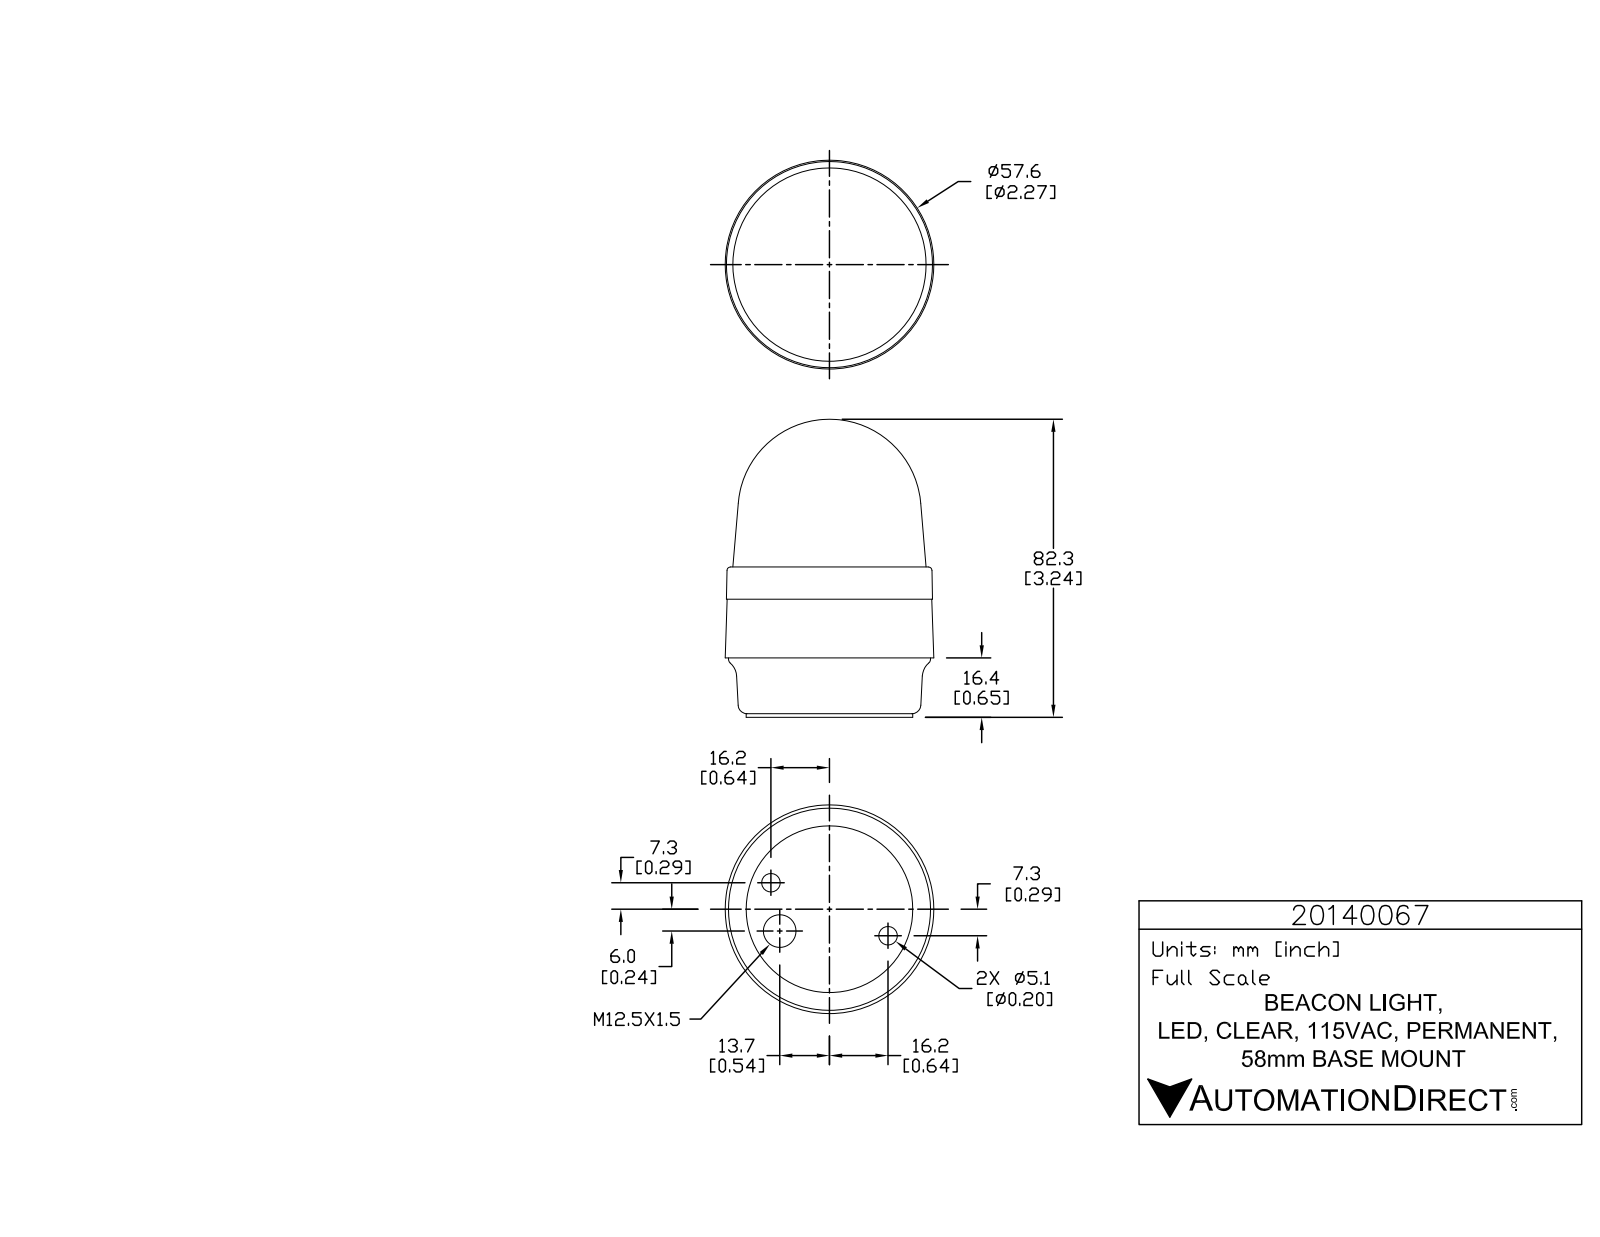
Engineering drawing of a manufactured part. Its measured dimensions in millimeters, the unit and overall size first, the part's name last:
Units: millimetres
Overall size (bounding box): 82.3 × 57.63 × 57.63
Round holes (diameter × count): ⌀0.99 ×3, ⌀5.11 ×2, ⌀9 ×1
Round bosses / shafts (diameter × count): ⌀5.74 ×3, ⌀1.43 ×3, ⌀55.8 ×1, ⌀46 ×1
Partial cylindrical surfaces — rounded edges, fillets, slot ends (radius × count): R0.2 ×6, R0.21 ×6, R0.21 ×6, R3.32 ×6, R0.1 ×3, R0.12 ×3, R0.19 ×3, R0.2 ×3
Main face-to-face distances: 16.4, 1, 15.4, 41.5, 40.5, 25.1, 32.6, 31.6, 16.2, 8.9
Hole centre spacings: 13.56, 29.94, 35.5
Volume: 164 395 mm³ · Surface area: 16 261 mm²
Bodies: 1 solid, 763 faces (527 planar, 145 cylindrical, 91 other)
Part name (STEP PRODUCT): 20140067
STEP written by: SolidWorks 2015 (AUTOMOTIVE_DESIGN)
